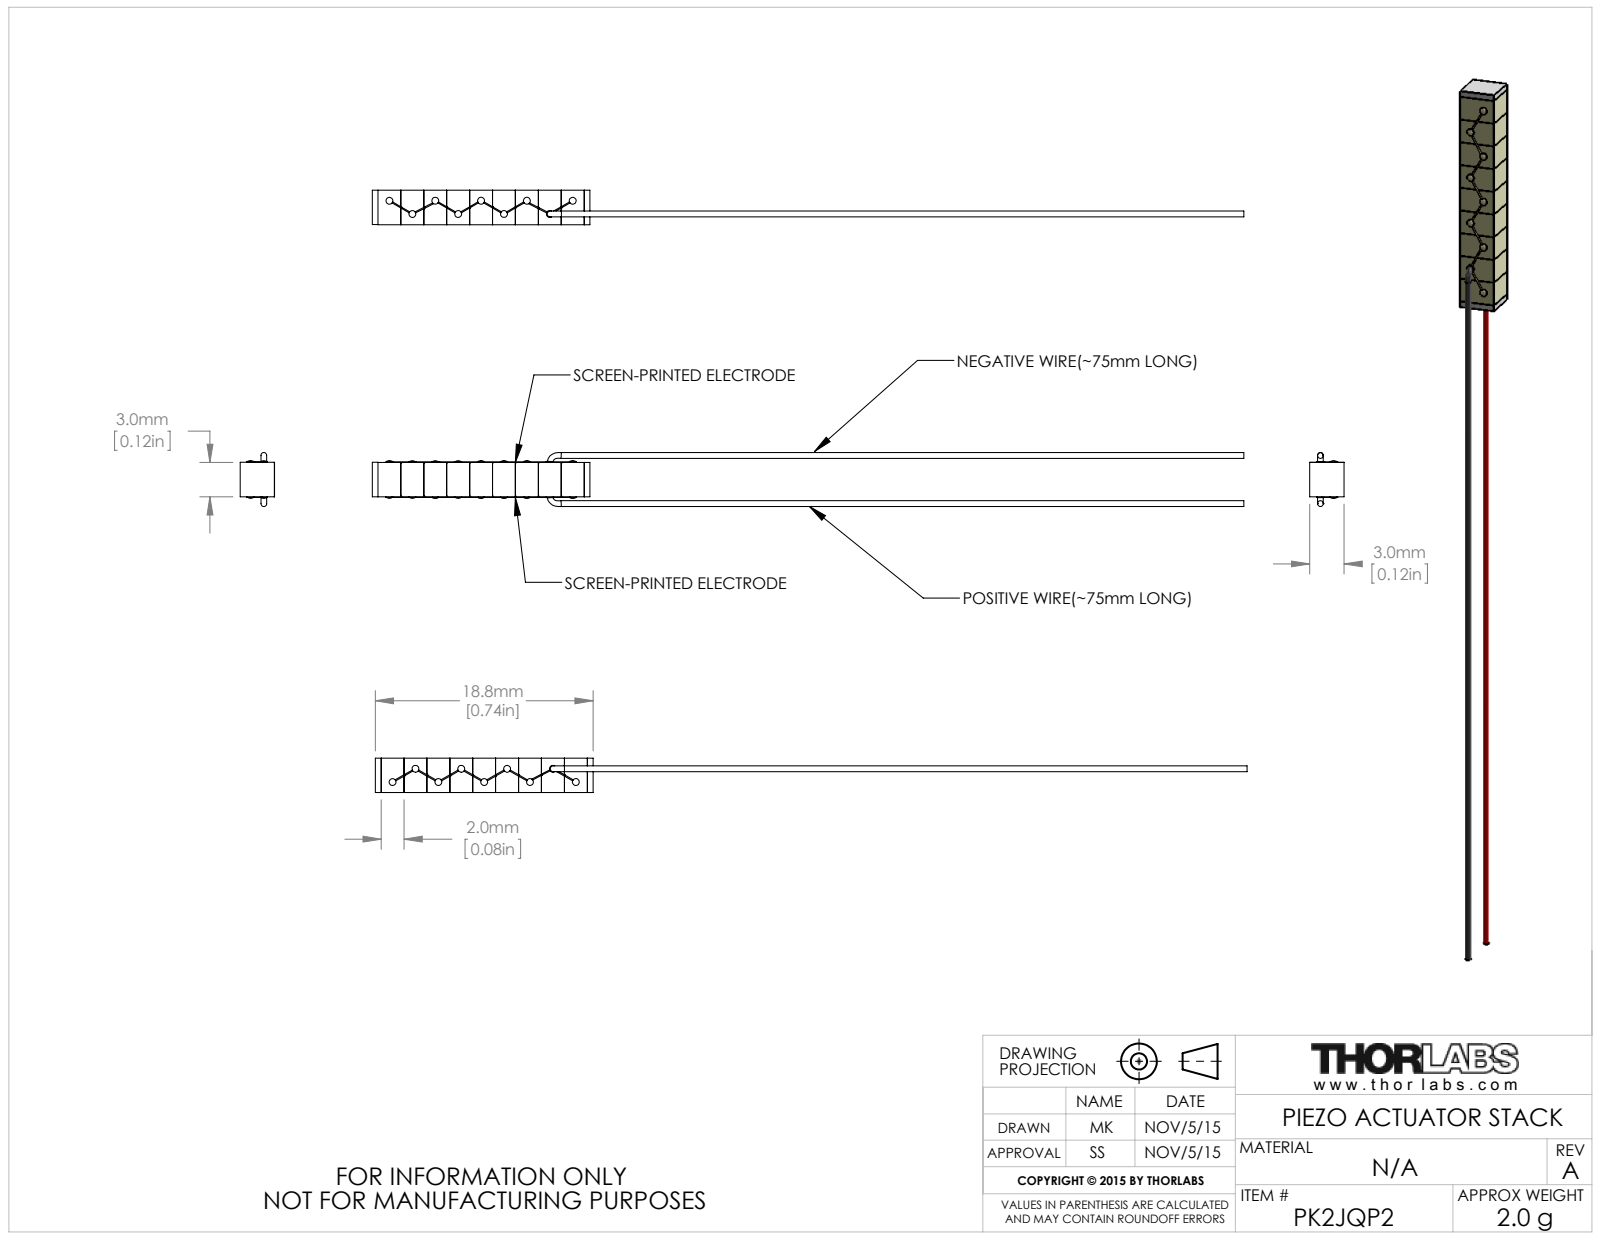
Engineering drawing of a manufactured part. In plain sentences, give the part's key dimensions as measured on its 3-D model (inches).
The part is named "CTN003187". Its 3-D file was written by "SolidWorks 2014 (AUTOMOTIVE_DESIGN)". It is 3 solids with 203 faces: 82 planar, 83 cylindrical and 38 other. Overall it measures 2.996 by 0.186 by 0.118 inches. Its volume is 0.012 cubic inches and its surface area 0.964 square inches. Round bosses or shafts: 9 of diameter 0.024. The main face-to-face distances are 0.079, 0.157, 0.236, 0.118, 0.315, 0.394, 0.472, 0.551, 0.63, 0.02.
